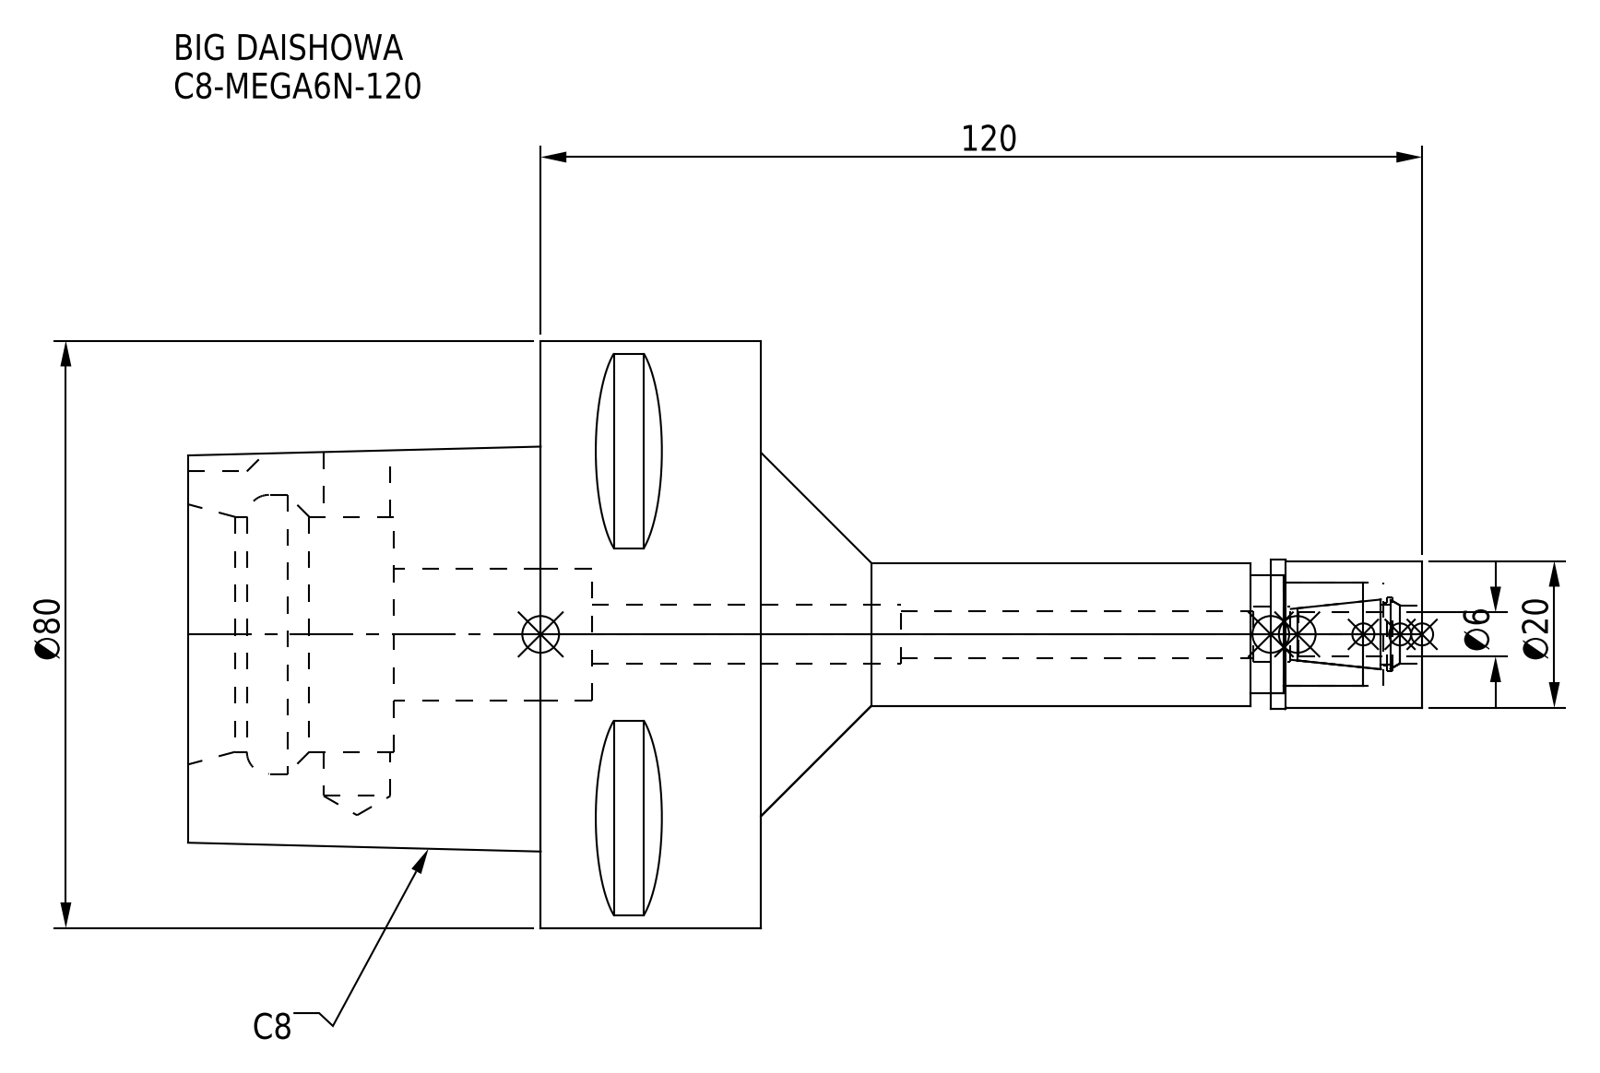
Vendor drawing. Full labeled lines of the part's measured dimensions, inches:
Part name (STEP PRODUCT): C8-MEGA6N-120_1.stp; C8-MEGA6N-120; DXF_TEMP_ASSY_ASM_4_ASM.stp; C8-MEGA6N-120-060-FreeParts (+3 more)
STEP written by: SolidWorks 2019 (CONFIG_CONTROL_DESIGN)
Units: inches
Bodies: 2 solids, 98 faces (39 planar, 41 cylindrical, 18 other)
Overall size (bounding box): 6.614 × 3.15 × 3.15
Volume: 15.59 in³ · Surface area: 62.9 in²
Round holes (diameter × count): ⌀0.252 ×1, ⌀0.295 ×1, ⌀0.311 ×1, ⌀0.315 ×1, ⌀0.335 ×1, ⌀0.358 ×1, ⌀0.394 ×1, ⌀0.551 ×1, ⌀0.63 ×1, ⌀0.709 ×1, ⌀1.26 ×1, ⌀1.496 ×1
Round bosses / shafts (diameter × count): ⌀3.15 ×1, ⌀0.799 ×1, ⌀0.787 ×1, ⌀0.768 ×1
Partial cylindrical surfaces — rounded edges, fillets, slot ends (radius × count): R0.236 ×1
Main face-to-face distances: 1.181, 1.89, 3.071, 0.787, 1.969, 1.102, 1.281, 2.783, 3.543, 4.724
